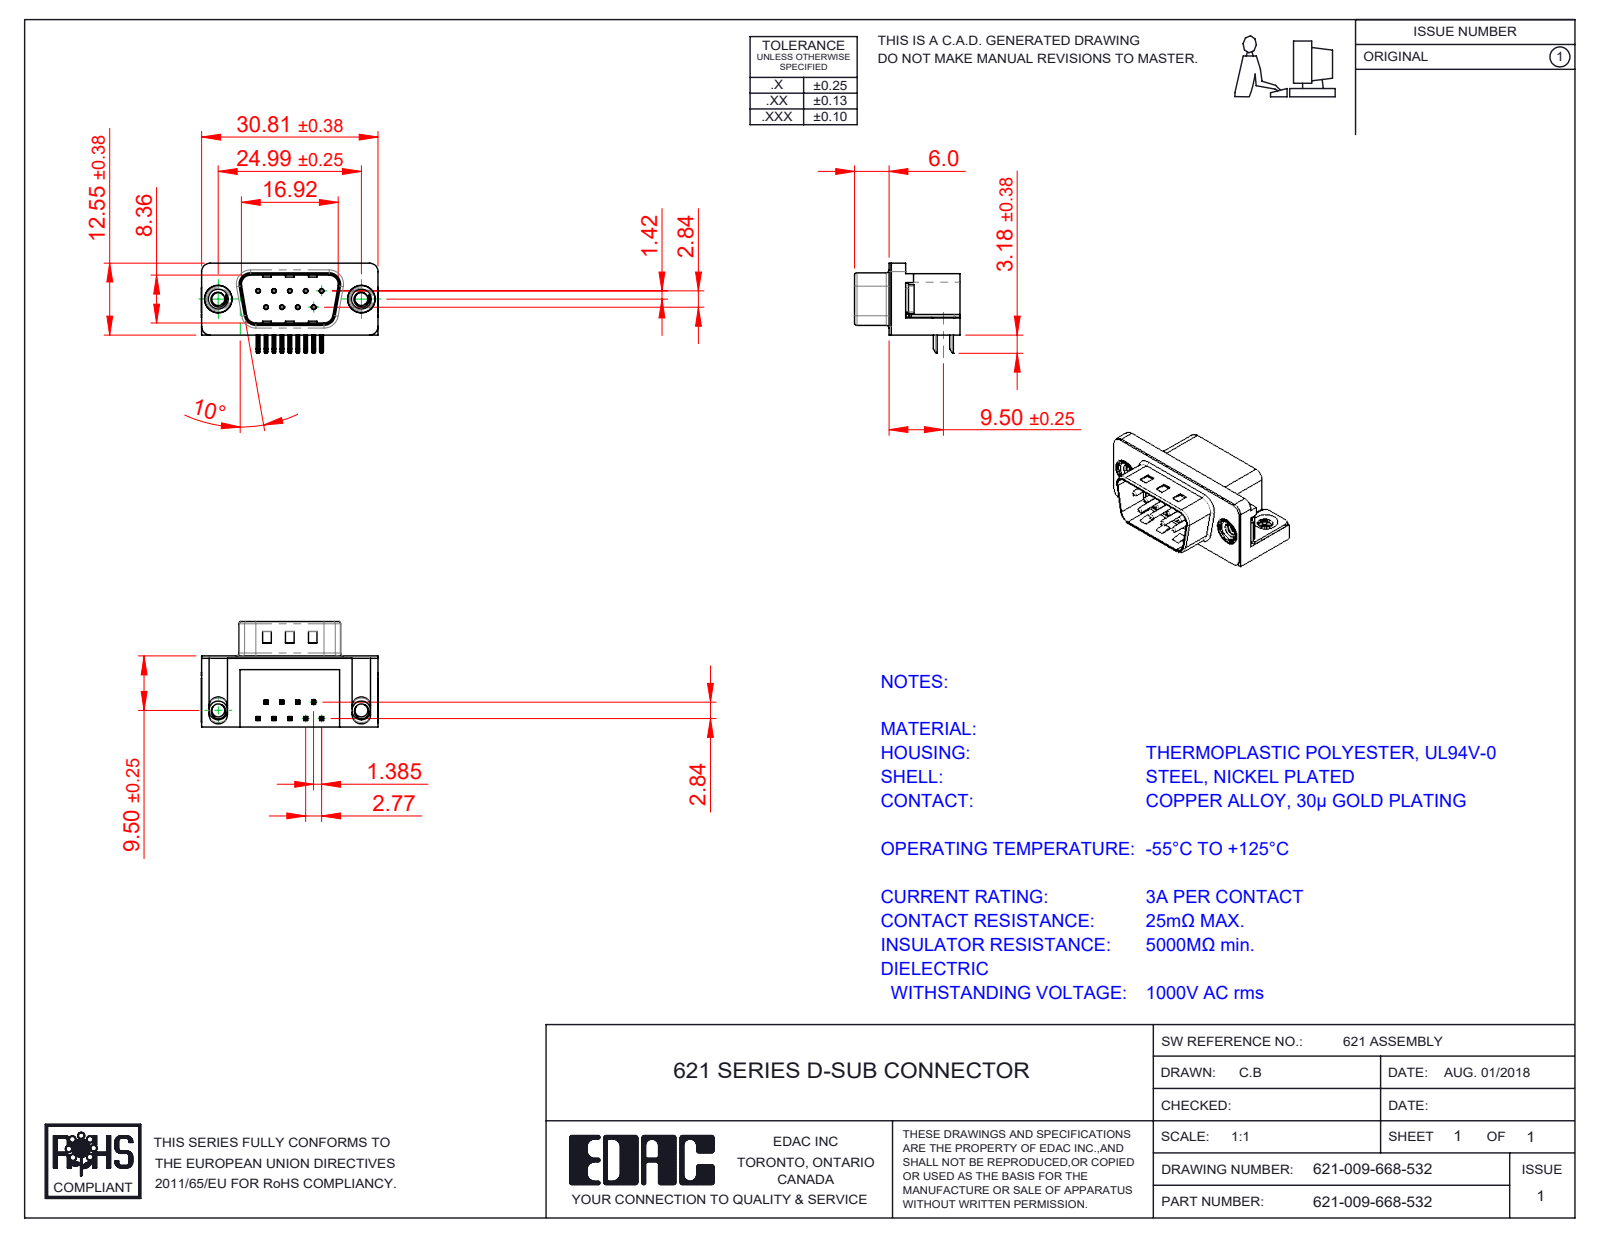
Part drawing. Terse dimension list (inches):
name: 621 Contact Top; 621 Contact Bottom; 621-009-668-532; 621 Shell_9 Socket (+3 more)
written by: SolidWorks 2016 (CONFIG_CONTROL_DESIGN)
unit: in
bodies: 15 solids, 1031 faces (605 planar, 323 cylindrical, 103 other)
size: 1.216 × 0.724 × 0.64
volume: 0.198 in³; area: 6.862 in²
holes: 9× ⌀0.014, 9× ⌀0.031, 2× ⌀0.089, 2× ⌀0.157, 2× ⌀0.189, 2× ⌀0.197
bosses: 9× ⌀0.03, 2× ⌀0.193, 2× ⌀0.187, 2× ⌀0.154
rounds: 44× R0.01, 18× R0.005, 16× R0.039, 14× R0.02, 8× R0.059, 8× R0.063, 4× R0.013, 4× R0.035
face distances: 0.016, 0.472, 0.488, 0.407, 0.02, 0.374, 0.098, 0.114, 0.083, 0.014
hole spacings: 0.124, 0.109, 0.218, 0.198, 0.198, 0.327, 0.294, 0.295
